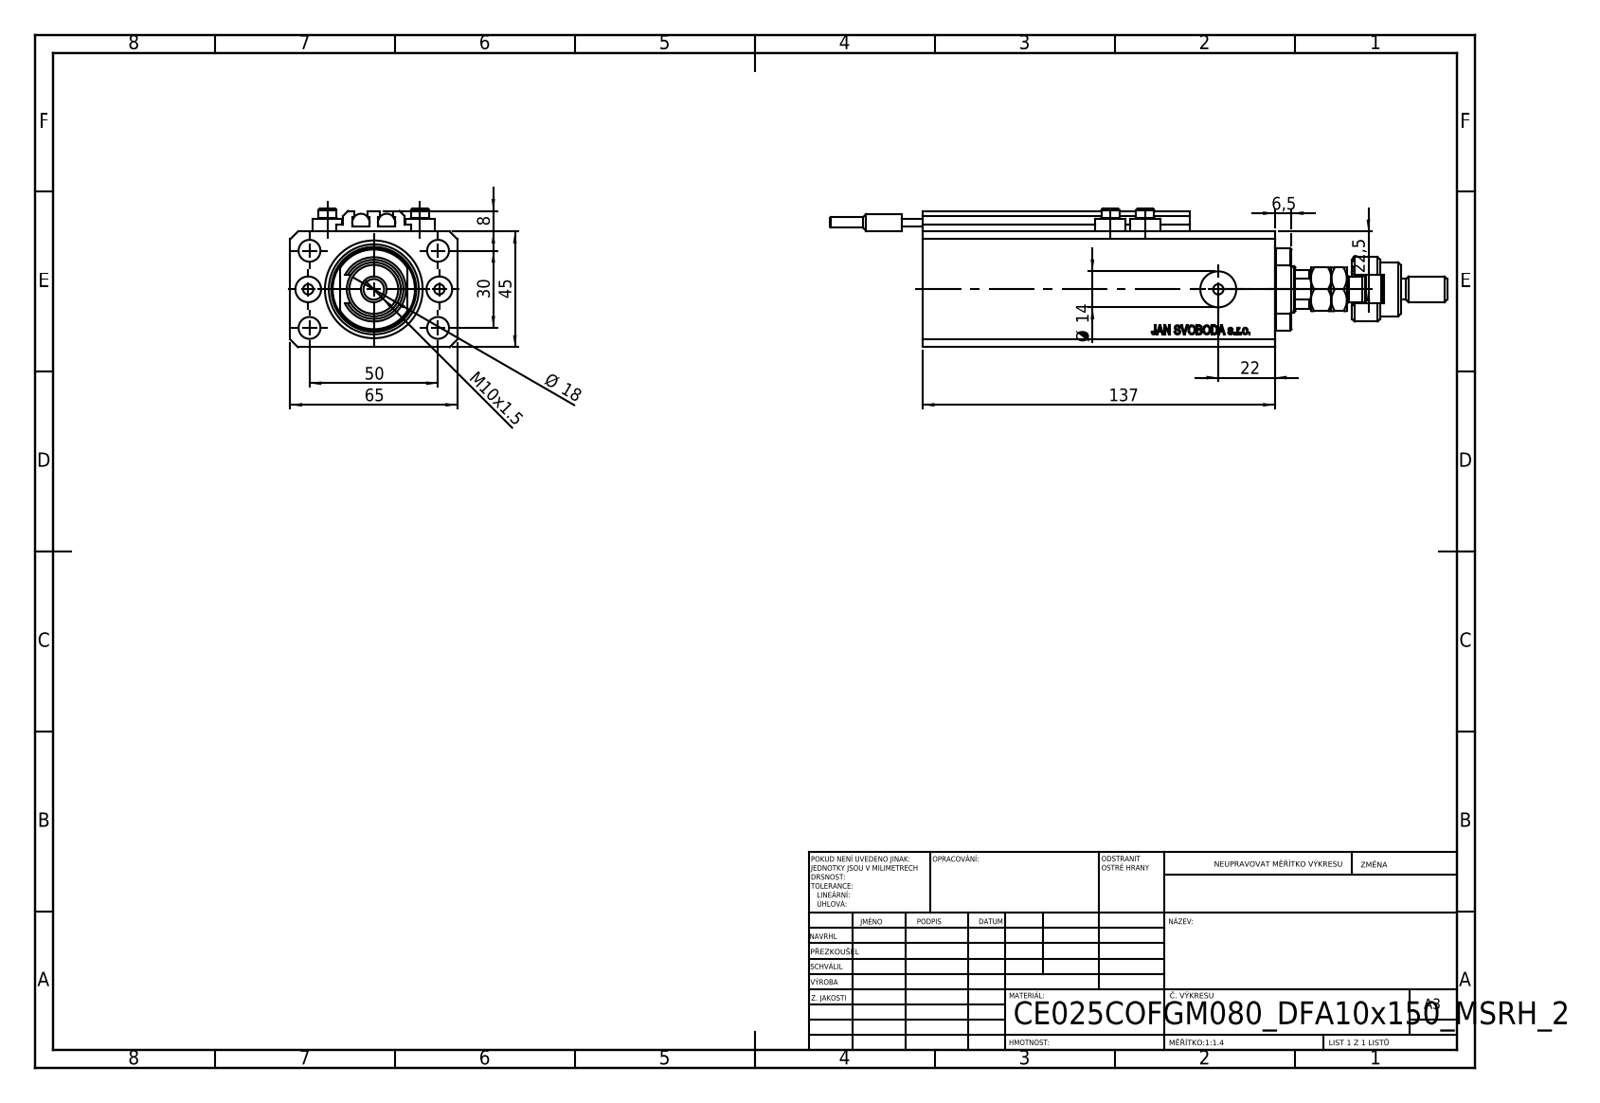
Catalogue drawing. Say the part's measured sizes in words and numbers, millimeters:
The part is named "V250CE_C_Body; SWITCH_V250CE; MFA; V250CE_C_VCP (+3 more)". Its 3-D file was written by "SolidWorks 2019 (CONFIG_CONTROL_DESIGN)". It is 12 solids with 1171 faces: 564 planar, 111 cylindrical and 496 other. Overall it measures 240 by 65 by 54 millimeters. Its volume is 381 494 cubic millimeters and its surface area 98 801 square millimeters. Round holes: 8 of diameter 4, 5 of diameter 8.5, 2 of diameter 10, 2 of diameter 14, 1 of diameter 18, 1 of diameter 38. Round bosses or shafts: 4 of diameter 11.6, 4 of diameter 7, 2 of diameter 6.8, 2 of diameter 6.5, 2 of diameter 4, 1 of diameter 25, 1 of diameter 21, 1 of diameter 16. Partial cylindrical surfaces (rounded edges, fillets, slot ends): 10 of radius 0.2, 1 of radius 5.5, 1 of radius 8.5, 1 of radius 8.75, 1 of radius 16. The main face-to-face distances are 45, 65, 14, 47, 2, 3, 123, 2.5, 137, 10. The hole center spacings are 15.01, 29.15, 52.68, 13.6, 25.5, 30, 36, 38.48.
